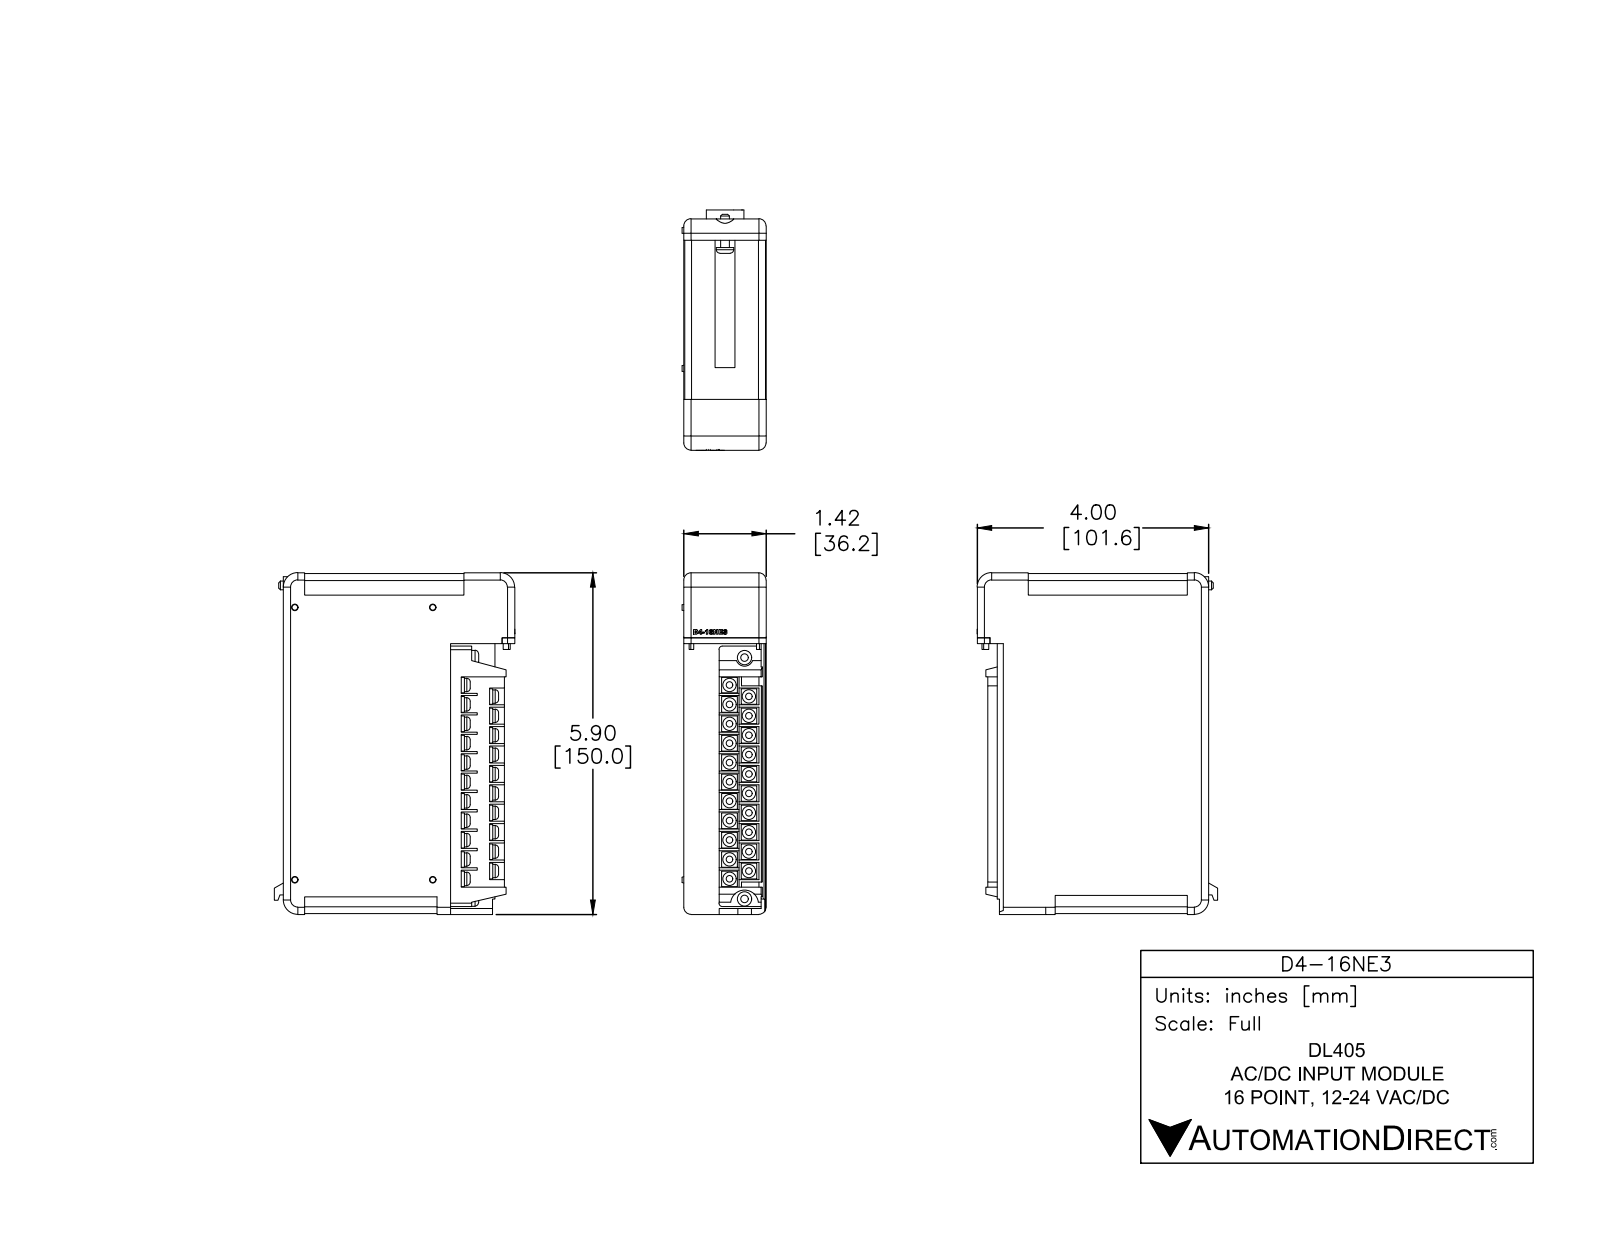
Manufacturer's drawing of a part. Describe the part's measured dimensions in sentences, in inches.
The part is named "D4-16NE3". Its 3-D file was written by "SolidWorks 2014 (AUTOMOTIVE_DESIGN)". It is 14 solids with 606 faces: 421 planar, 86 cylindrical and 99 other. Overall it measures 5.905 by 4.156 by 1.455 inches. Its volume is 27.51 cubic inches and its surface area 86.82 square inches. Round bosses or shafts: 21 of diameter 0.23, 2 of diameter 0.25, 1 of diameter 0.3, 1 of diameter 0.15. Partial cylindrical surfaces (rounded edges, fillets, slot ends): 8 of radius 0.125, 4 of radius 0.12, 3 of radius 0.25, 2 of radius 0.015, 2 of radius 0.03, 2 of radius 0.06, 1 of radius 0.149, 1 of radius 0.151. The main face-to-face distances are 1.425, 0.015, 2.89, 5.875, 1.41, 0.47, 0.2, 0.955, 5.89, 1.21.
